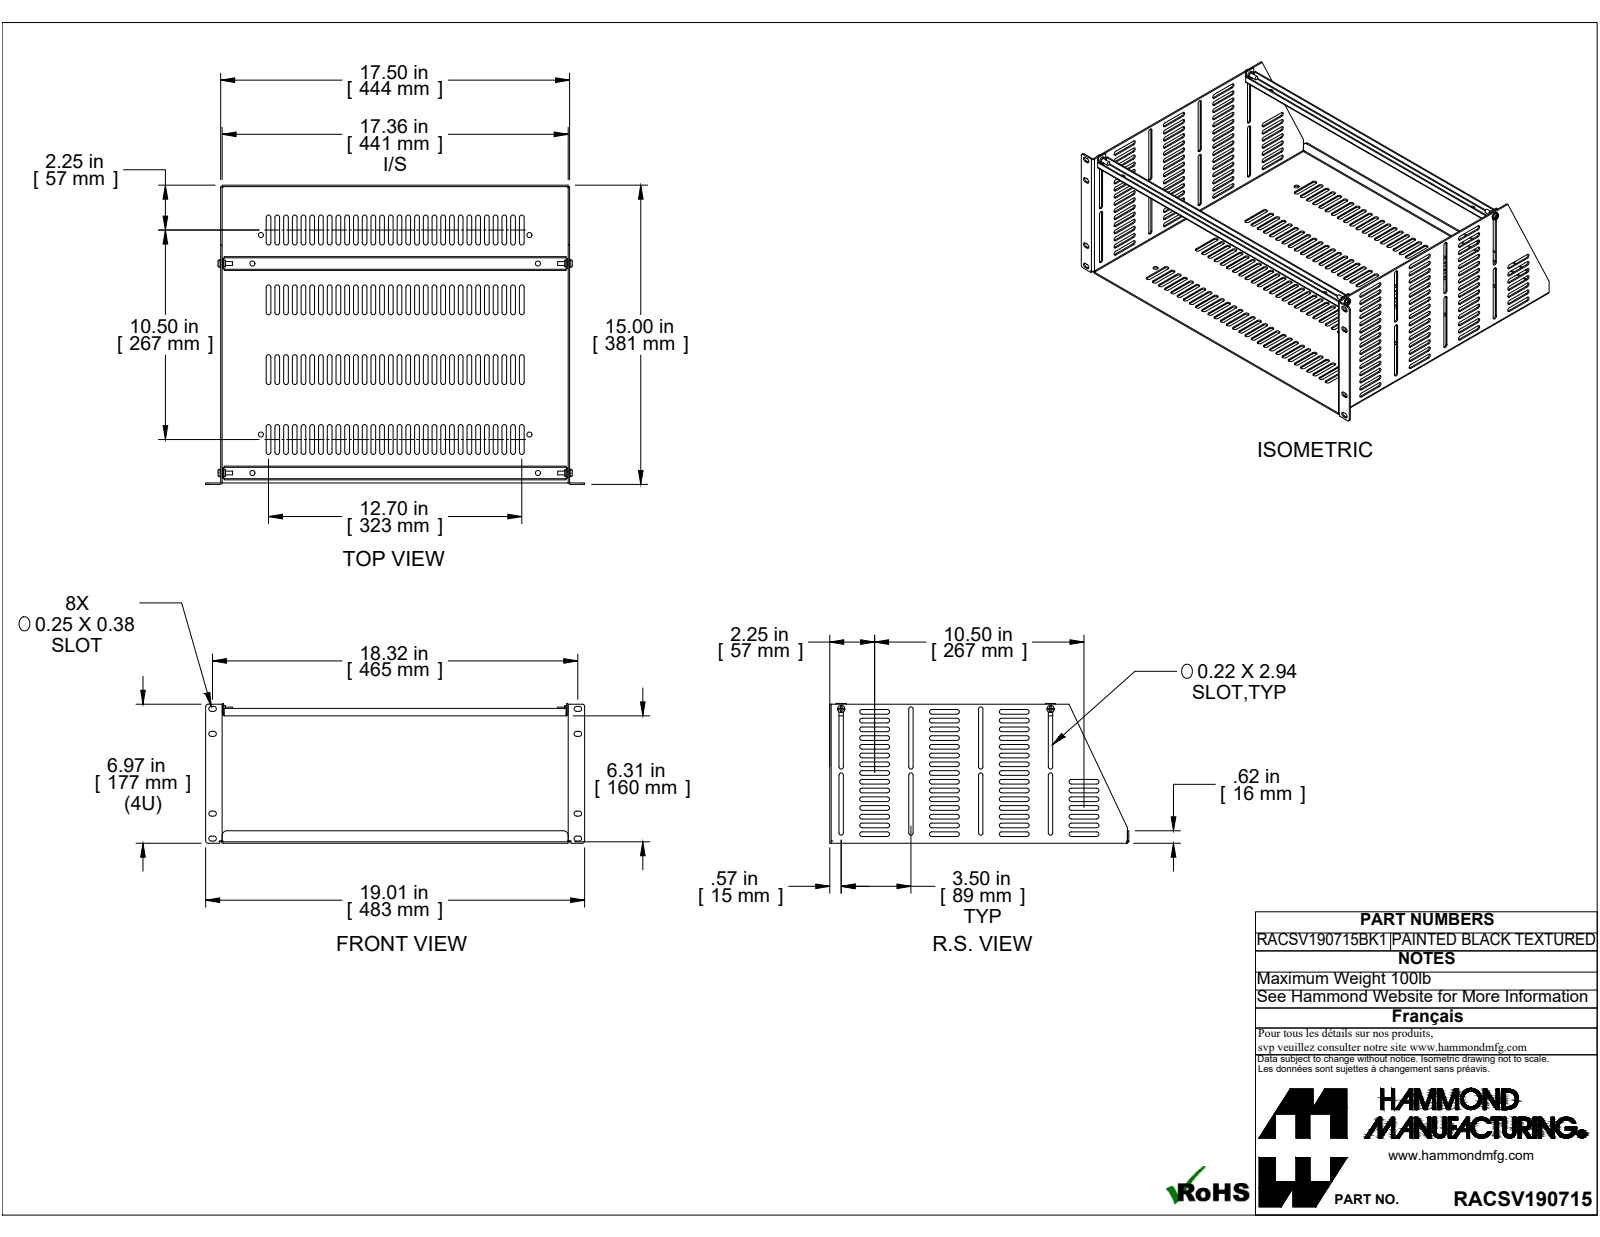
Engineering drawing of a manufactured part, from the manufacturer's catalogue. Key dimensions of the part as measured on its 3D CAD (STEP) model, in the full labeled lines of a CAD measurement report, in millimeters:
Part name (STEP PRODUCT): RACSV190715
STEP written by: SolidWorks 2019 (CONFIG_CONTROL_DESIGN)
Units: millimetres
Bodies: 11 solids, 1242 faces (662 planar, 564 cylindrical, 16 other)
Overall size (bounding box): 482.8 × 381 × 178
Volume: 491 600 mm³ · Surface area: 596 700 mm²
Round holes (diameter × count): ⌀6.4 ×6, ⌀4 ×2
Round bosses / shafts (diameter × count): ⌀9.3 ×2, ⌀8.6 ×2, ⌀6.2 ×2, ⌀4.8 ×2
Partial cylindrical surfaces — rounded edges, fillets, slot ends (radius × count): R3 ×330, R3.2 ×20, R2.8 ×16, R3 ×14, R0.7 ×6, R2.2 ×6, R0.9 ×5, R2.7 ×5
Main face-to-face distances: 1.8, 442.7, 444.5, 440.8, 1.4, 266.7, 16, 162.2, 163.6, 160.4
Hole centre spacings: 254, 342.1, 426.1, 266.7
